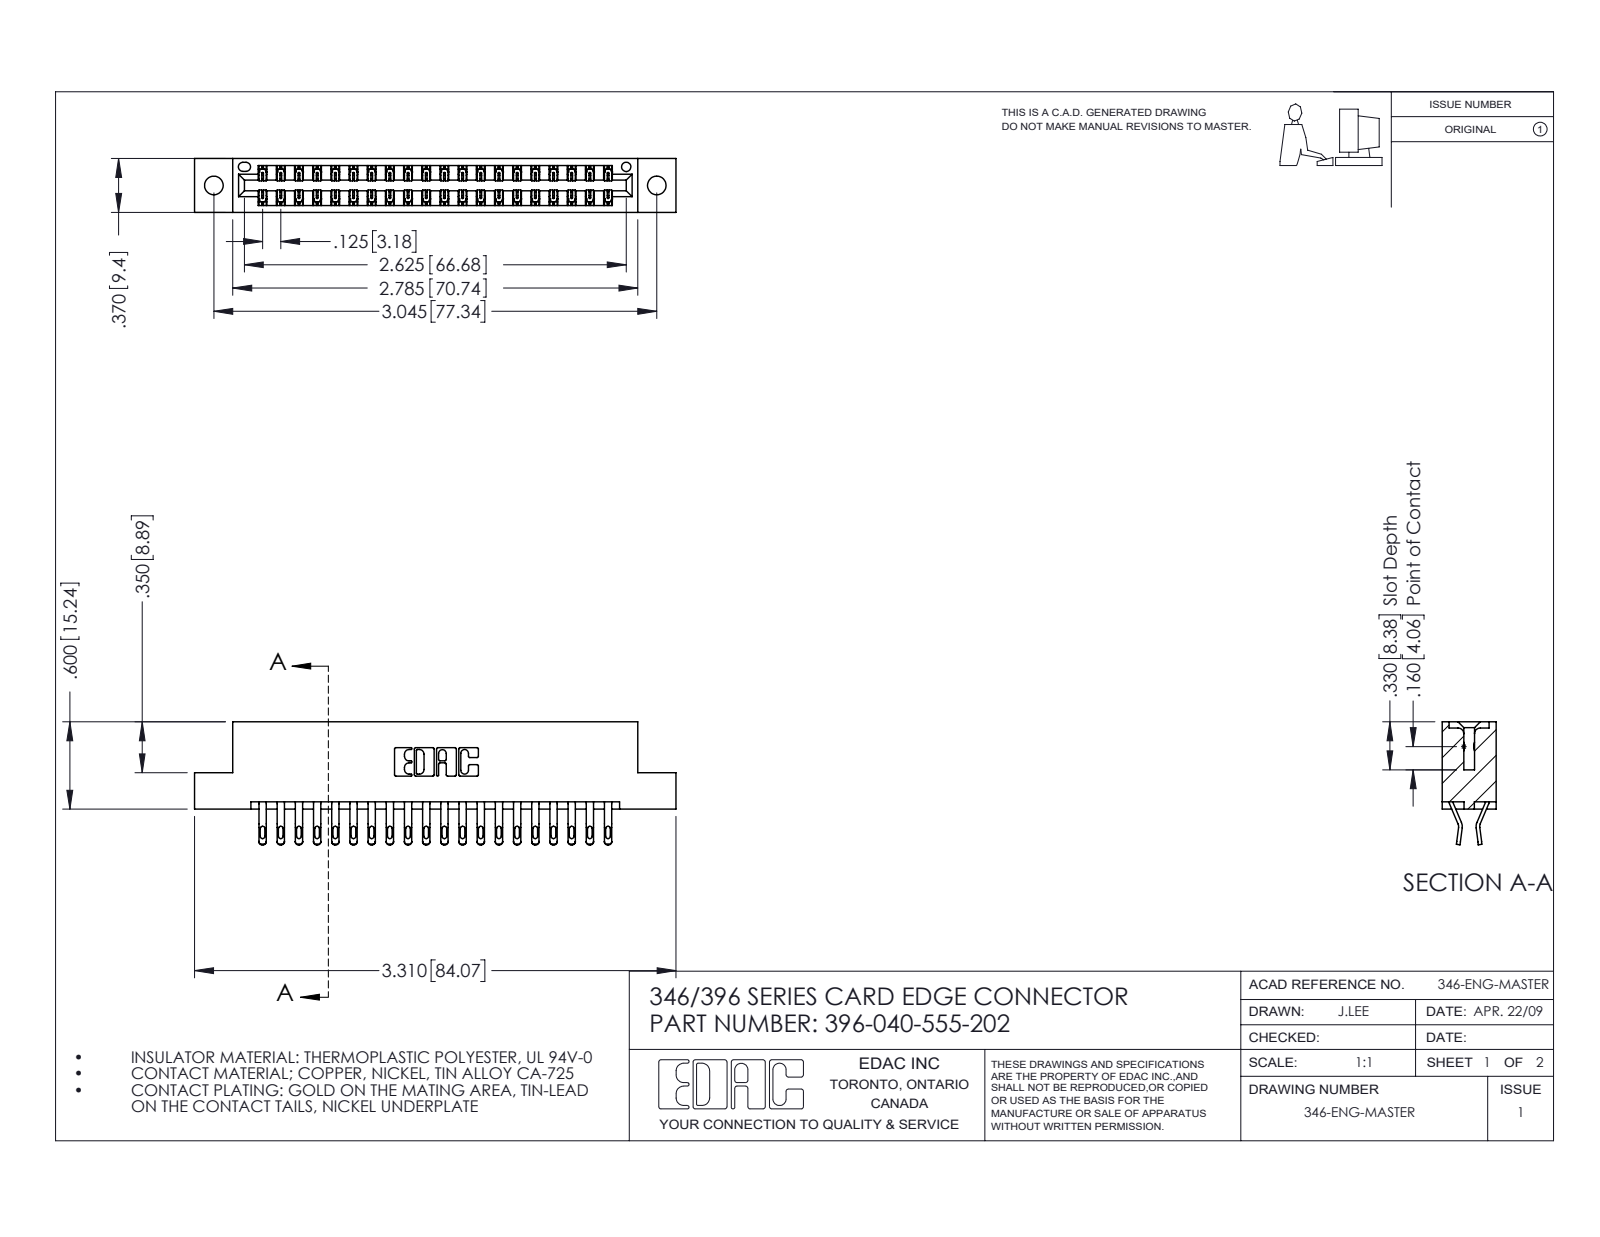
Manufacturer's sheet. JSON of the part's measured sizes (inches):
{"part_name": "396-040-555-202; 345-292-001_555 Tail; 346 Part_Flush Mounting Lugs - 0.128 Dia", "step_written_by": "SolidWorks 2016 (CONFIG_CONTROL_DESIGN)", "units": "inches", "bodies": {"solids": 41, "faces": 2442, "planar": 1396, "cylindrical": 1046, "other": 0}, "overall_size": [3.31, 0.845, 0.37], "volume_in3": 0.495, "surface_area_in2": 16.96, "round_holes": [[0.128, 2], [0.064, 1]], "partial_cylinders_radius": [[0.016, 80], [0.02, 80], [0.006, 60], [0.01, 22], [0.007, 6], [0.031, 6], [0.026, 3], [0.01, 2]], "face_to_face_distances": [0.048, 0.322, 0.25, 0.37, 0.025, 0.072, 0.298, 0.275, 0.148, 0.222], "hole_center_spacings": [0.246, 2.837, 3.045]}
